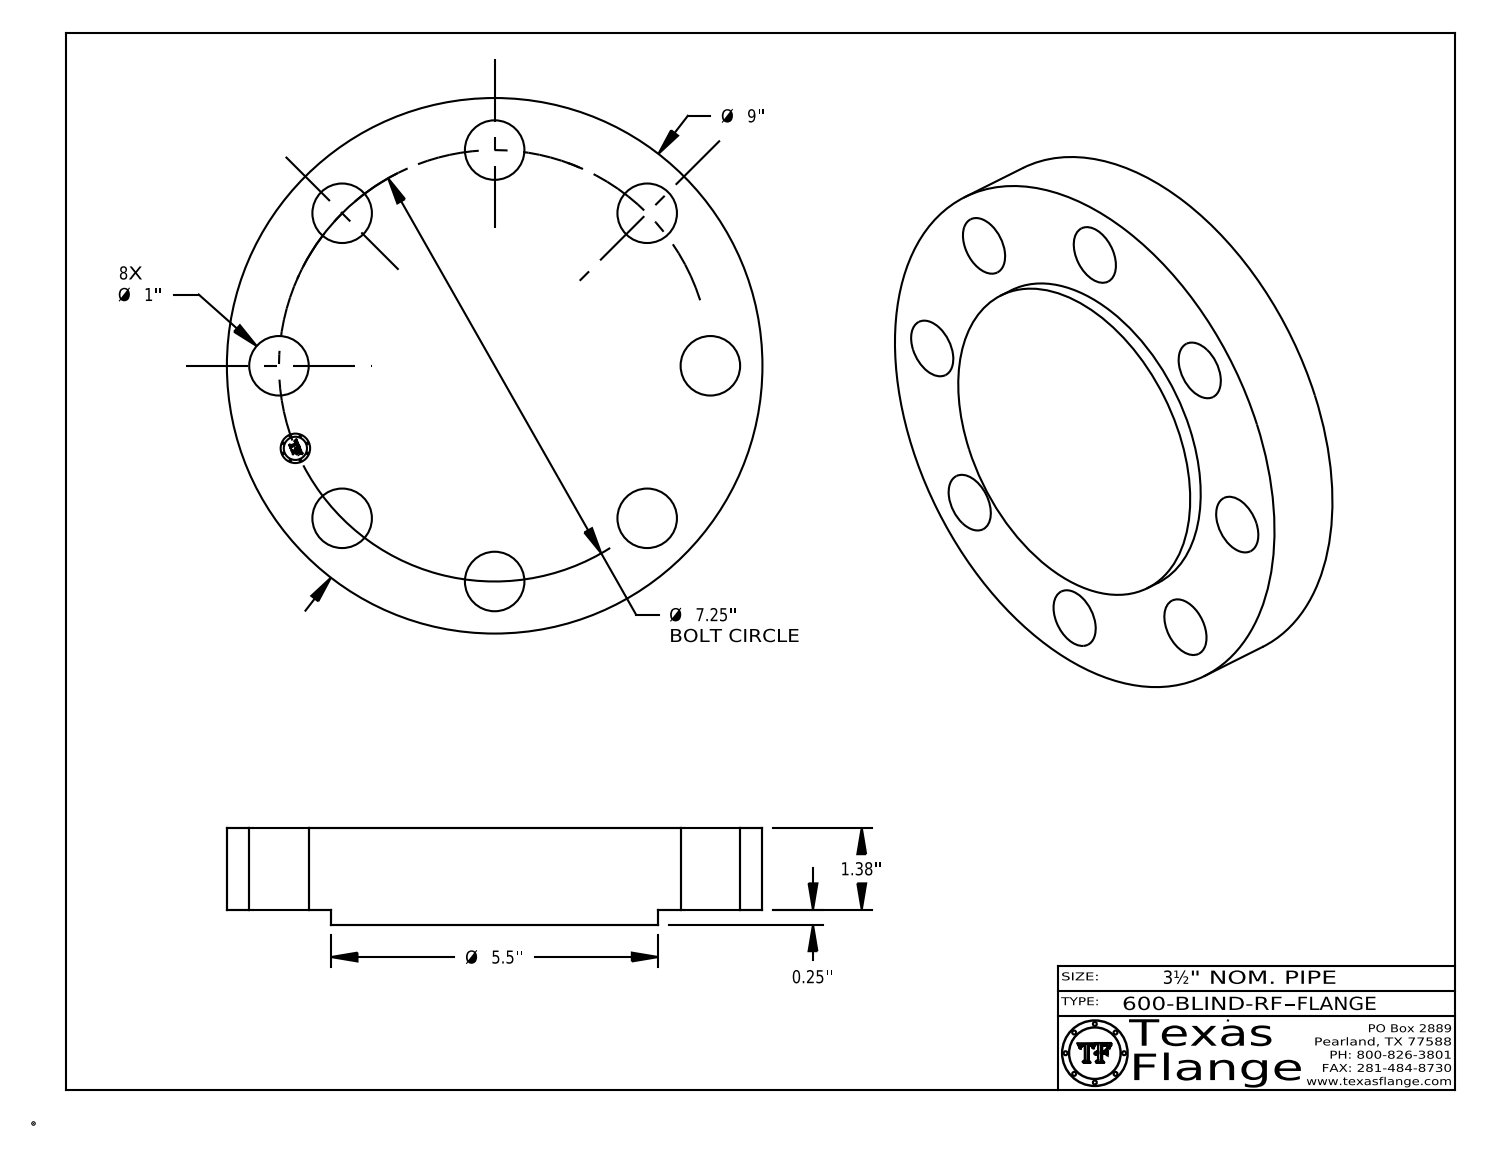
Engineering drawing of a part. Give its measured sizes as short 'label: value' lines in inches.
name: 600-BLIND-RF
written by: CATIA V5 STEP AP214 (AUTOMOTIVE_DESIGN)
unit: in
bodies: 1 solid, 408 faces (368 planar, 40 cylindrical, 0 other)
size: 9 × 9 × 1.63
volume: 85.06 in³; area: 192.8 in²
holes: 8× ⌀1, 1× ⌀0.495
bosses: 8× ⌀0.03, 1× ⌀9, 1× ⌀5.5, 1× ⌀0.39
face distances: 1.38, 0.25, 1.63, 1.615, 1.365, 0.015, 0.148, 0.144, 0.027, 0.096
hole spacings: 2.774, 5.127, 6.698, 7.25, 1.415, 7.111, 4.028, 4.028
